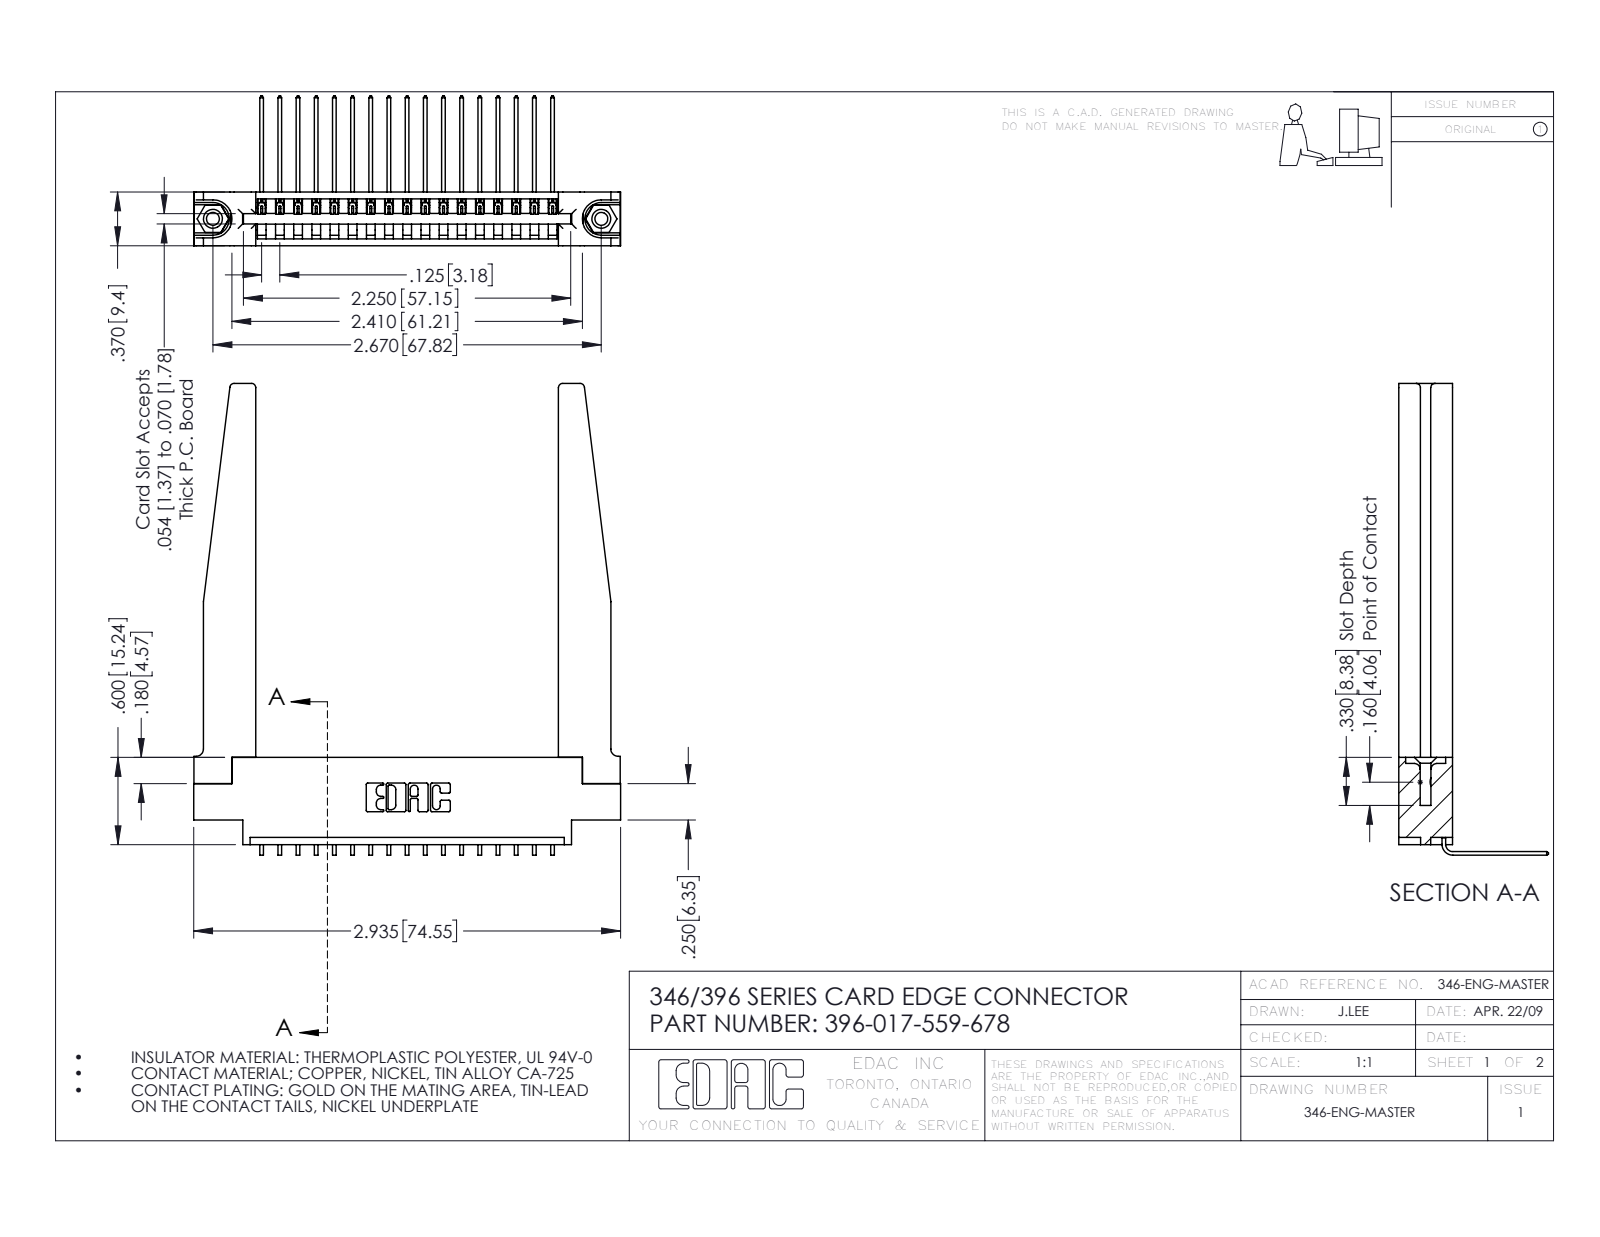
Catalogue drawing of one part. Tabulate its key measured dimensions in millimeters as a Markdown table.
| quantity | value |
| --- | --- |
| part name | 345-292-001_558 559 Tail - 1; 346-220-078_345-220-078; 396-017-559-678; 346 Part_0.170 Offset - 0.156 Dia-TH (+1 more) |
| STEP written by | SolidWorks 2016 (CONFIG_CONTROL_DESIGN) |
| units | millimeters |
| bodies | 22 solids, 1380 faces (936 planar, 392 cylindrical, 52 other) |
| overall size | 82.4 × 74.5 × 26.2 |
| volume | 13 800 mm³ |
| surface area | 15 350 mm² |
| round holes (diameter × count) | 2.3 × 2, 3.2 × 2, 4 × 2, 1.6 × 1 |
| round bosses / shafts (diameter × count) | 3.9 × 2 |
| partial cylindrical surfaces (radius × count) | 0.2 × 34, 0.3 × 22, 0.8 × 8, 0.2 × 6, 0.8 × 6, 0.7 × 3, 1.3 × 3, 0.8 × 2 |
| main face-to-face distances | 9.4, 1.8, 1.2, 3.8, 3.8, 8.2, 6.4, 0.6, 2.6, 5.6 |
| hole center spacings | 6.2, 62.6, 67.8 |
